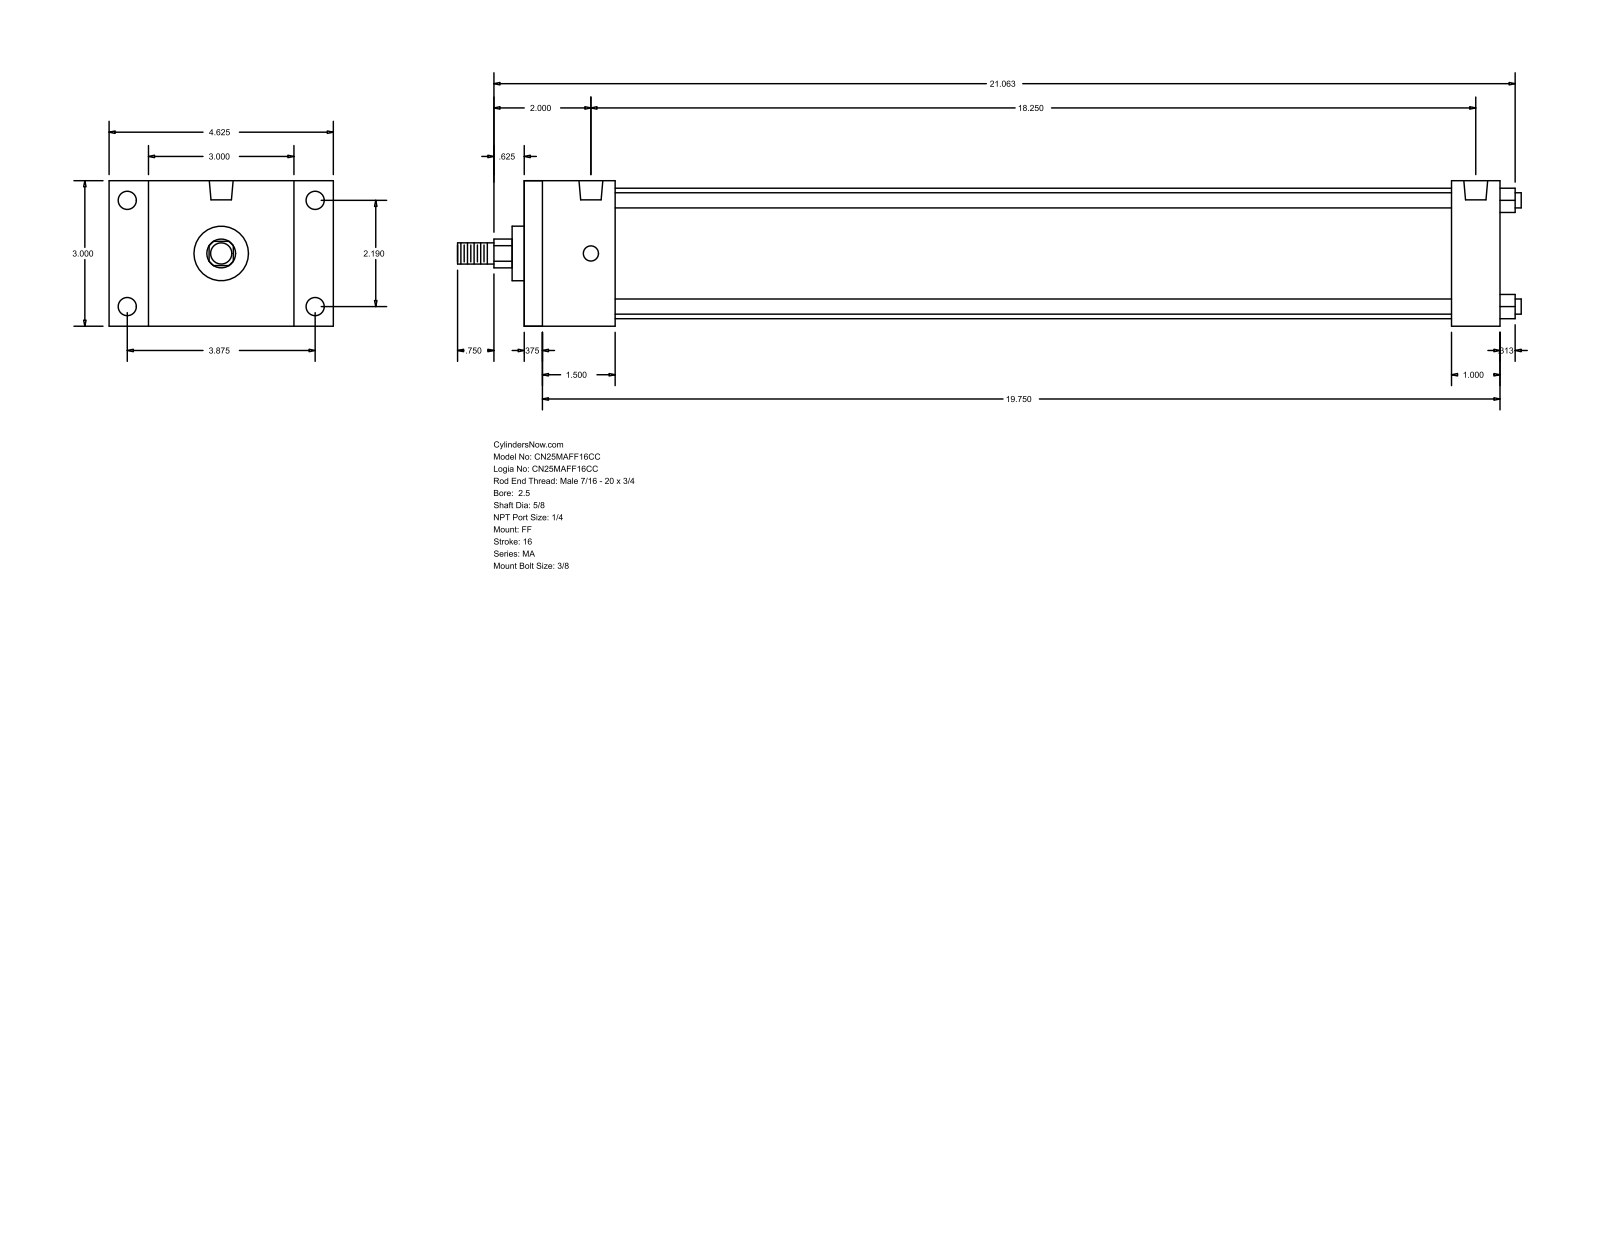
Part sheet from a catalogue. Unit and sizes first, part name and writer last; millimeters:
Units: millimetres
Overall size (bounding box): 557.21 × 117.47 × 76.2
Round holes (diameter × count): ⌀7.94 ×4, ⌀9.53 ×4, ⌀12.49 ×2
Round bosses / shafts (diameter × count): ⌀7.94 ×4, ⌀68.33 ×1, ⌀28.57 ×1, ⌀15.88 ×1, ⌀11.11 ×1
Partial cylindrical surfaces — rounded edges, fillets, slot ends (radius × count): R7.54 ×1
Main face-to-face distances: 76.2, 511.17, 501.65, 9.52, 25.4, 47.62, 485.77, 38.1, 476.25, 438.15
Hole centre spacings: 55.62, 98.42, 113.05, 463.55
Bodies: 0 solids, 92 faces (64 planar, 28 cylindrical, 0 other)
Part name (STEP PRODUCT): MA_FF__0250_0.625
STEP written by: GSSL Pune (CONFIG_CONTROL_DESIGN)
